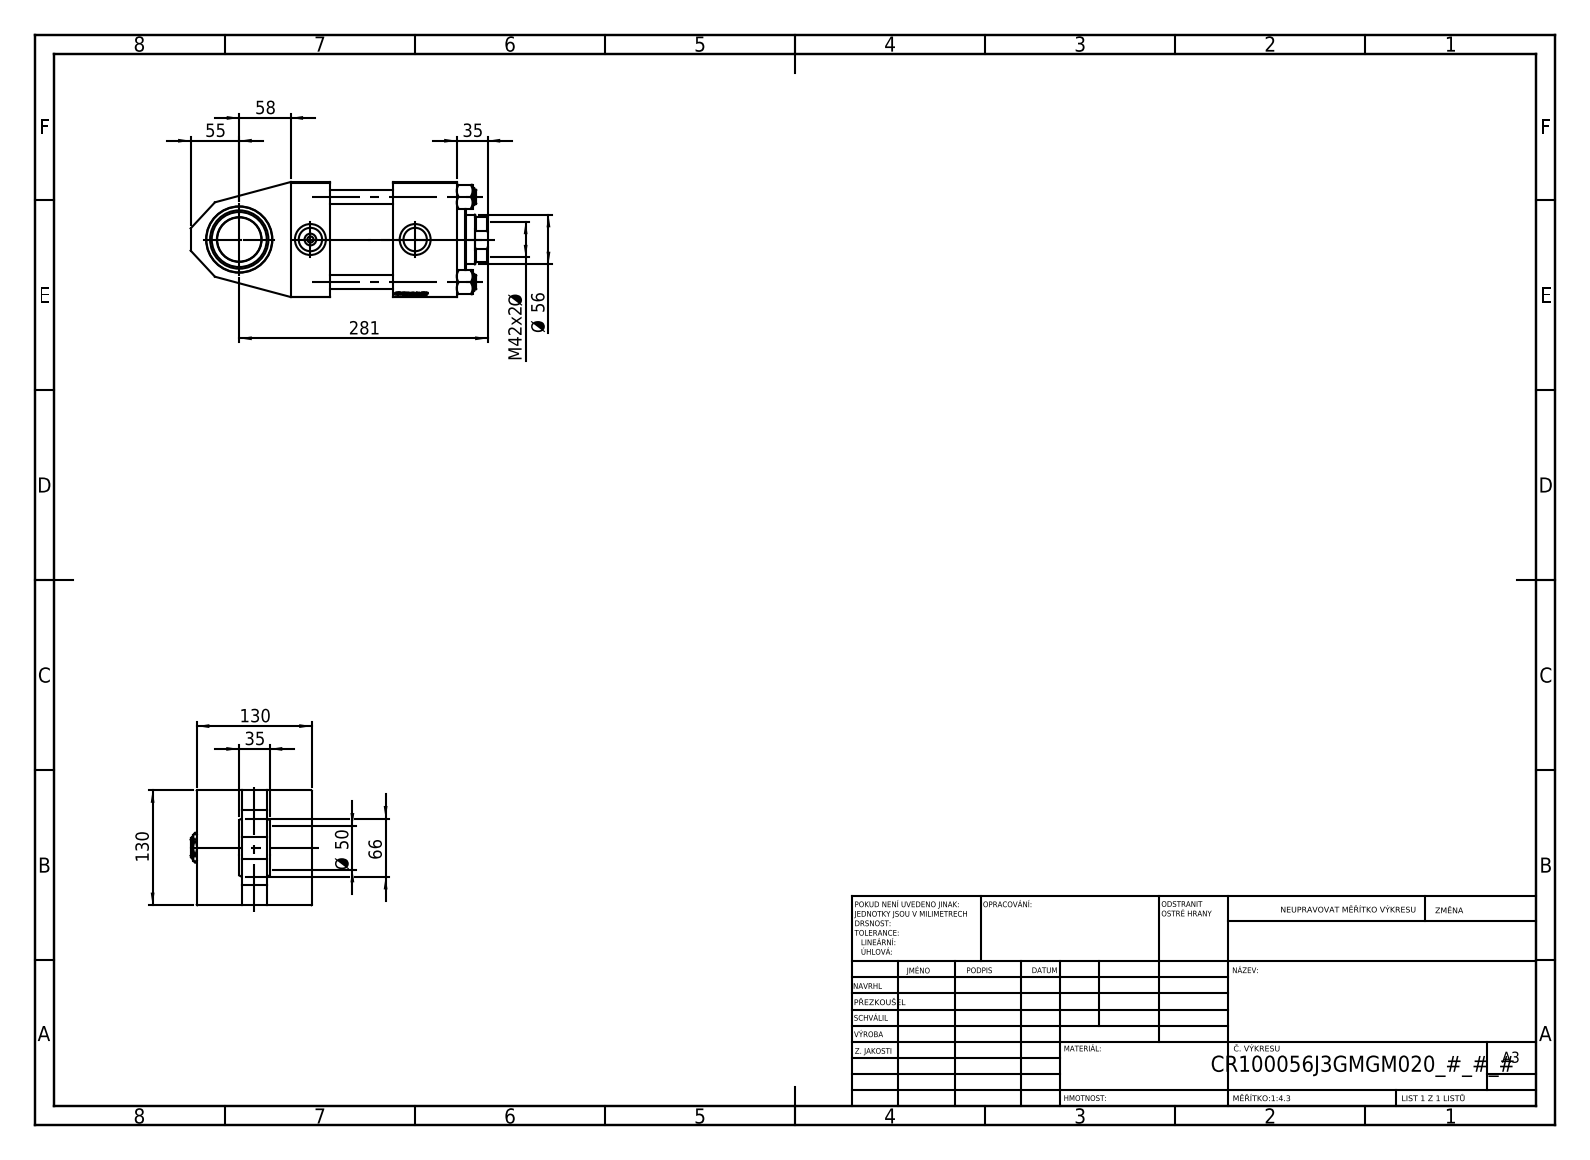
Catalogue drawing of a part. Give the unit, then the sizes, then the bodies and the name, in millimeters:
Units: millimetres
Overall size (bounding box): 336 × 137 × 130
Round holes (diameter × count): ⌀16 ×4, ⌀2.5 ×2, ⌀7 ×2, ⌀26.44 ×2, ⌀35 ×2, ⌀40.5 ×1, ⌀50 ×1, ⌀56 ×1, ⌀59 ×1, ⌀75 ×1, ⌀76 ×1, ⌀85.5 ×1
Round bosses / shafts (diameter × count): ⌀19 ×4, ⌀106 ×1, ⌀72 ×1
Partial cylindrical surfaces — rounded edges, fillets, slot ends (radius × count): R27 ×1
Main face-to-face distances: 130, 51, 79, 45, 188, 143, 71, 116, 72, 28
Hole centre spacings: 49.02, 68.52, 96.9, 101.73, 41, 137.04, 80.5, 82
Volume: 2 737 000 mm³ · Surface area: 386 389 mm²
Bodies: 14 solids, 1294 faces (612 planar, 100 cylindrical, 582 other)
Part name (STEP PRODUCT): V215CR_TYCINKA_J; V215CR_J_Body; NUT_M5_J; V215_VC_A (+3 more)
STEP written by: SolidWorks 2019 (CONFIG_CONTROL_DESIGN)
